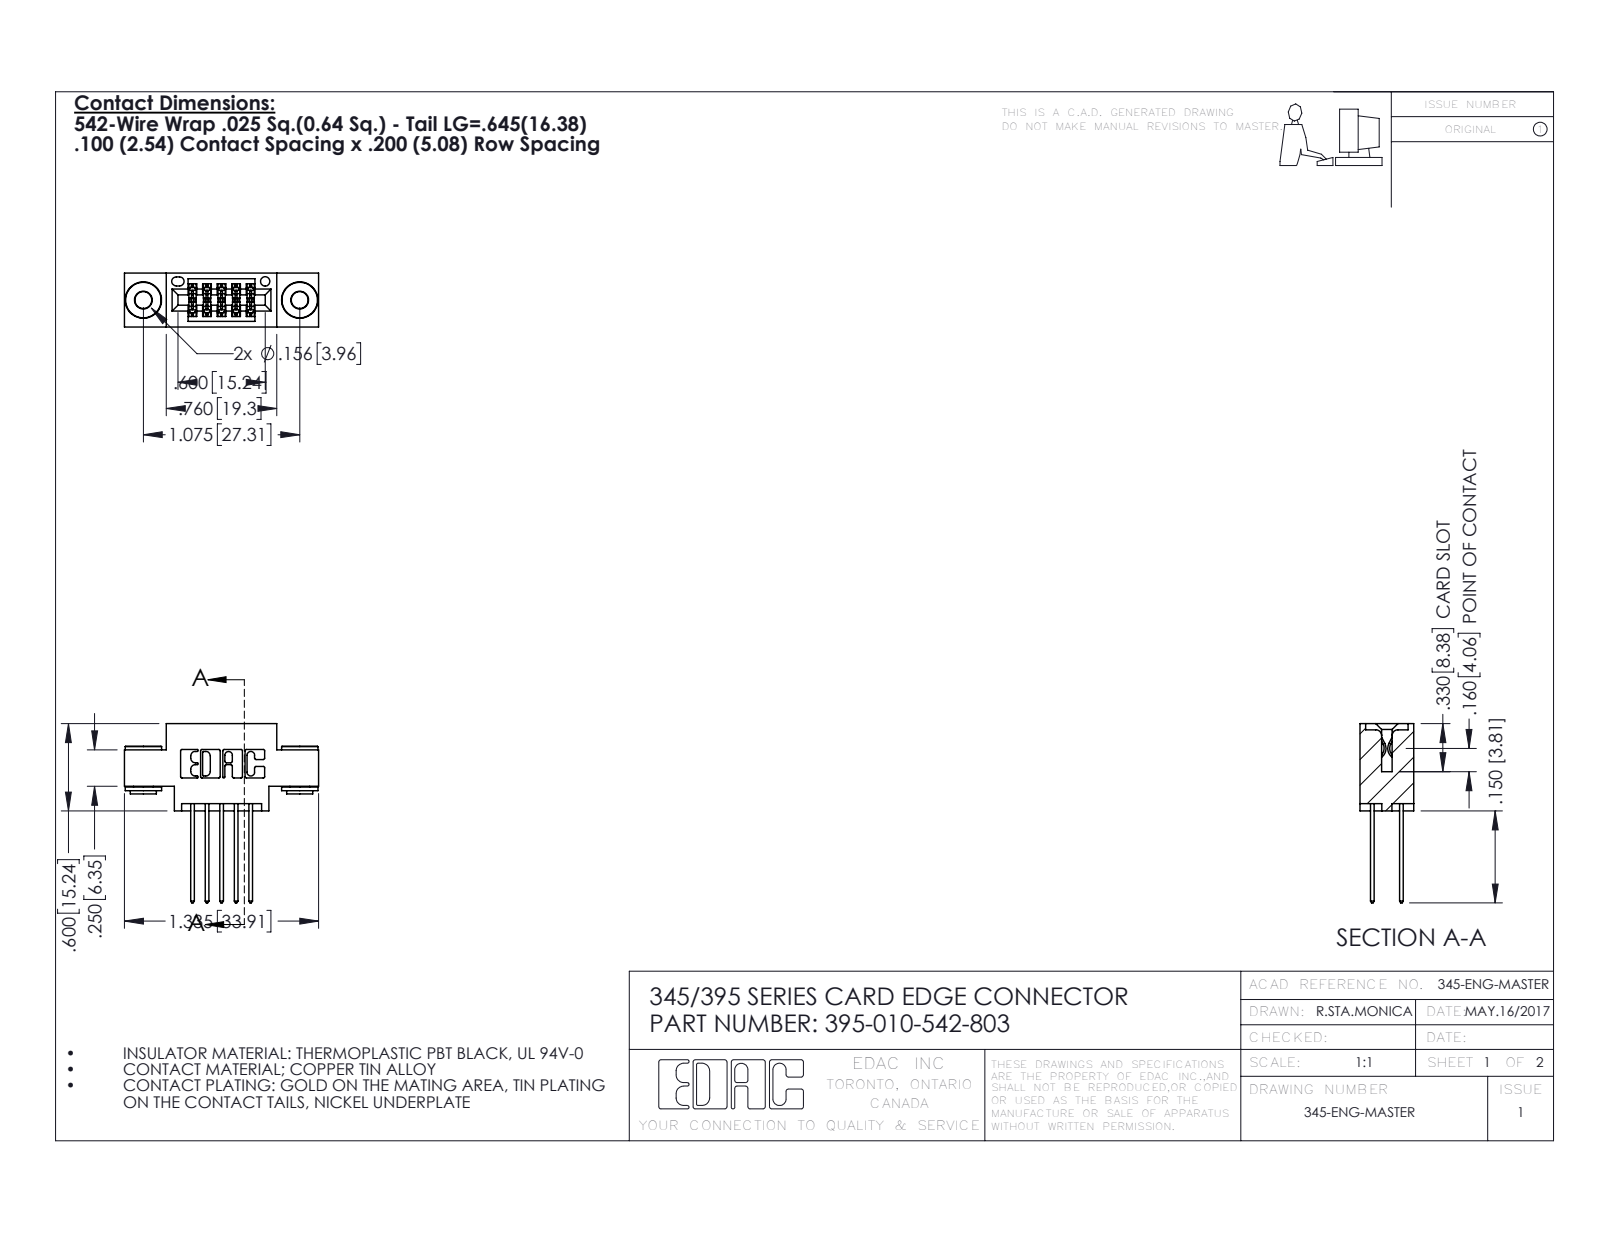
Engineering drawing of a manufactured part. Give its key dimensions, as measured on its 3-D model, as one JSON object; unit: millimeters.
{"part_name": "395-010-542-803; 345-292-001_345-293-142; 345-250-002_345-250-002-102; 345 Part_0.170 Offset - 0.156 Dia-TH", "step_written_by": "SolidWorks 2016 (CONFIG_CONTROL_DESIGN)", "units": "millimeters", "bodies": {"solids": 13, "faces": 668, "planar": 424, "cylindrical": 236, "other": 8}, "overall_size": [33.9, 31.3, 9.4], "volume_mm3": 2900, "surface_area_mm2": 4141, "round_holes": [[2.9, 2], [4, 2], [1.6, 1]], "round_bosses_or_shafts": [[6.4, 2], [4.6, 2], [3.5, 2]], "partial_cylinders_radius": [[0.3, 22], [0.2, 15], [0.3, 10], [0.2, 6], [0.8, 6], [0.7, 3], [0.4, 2], [0.5, 2]], "face_to_face_distances": [5.1, 9.4, 1.8, 7.6, 2.5, 2.5, 6.9, 0.6, 6.4, 5.7], "hole_center_spacings": [6.9, 21.5, 27.3]}
